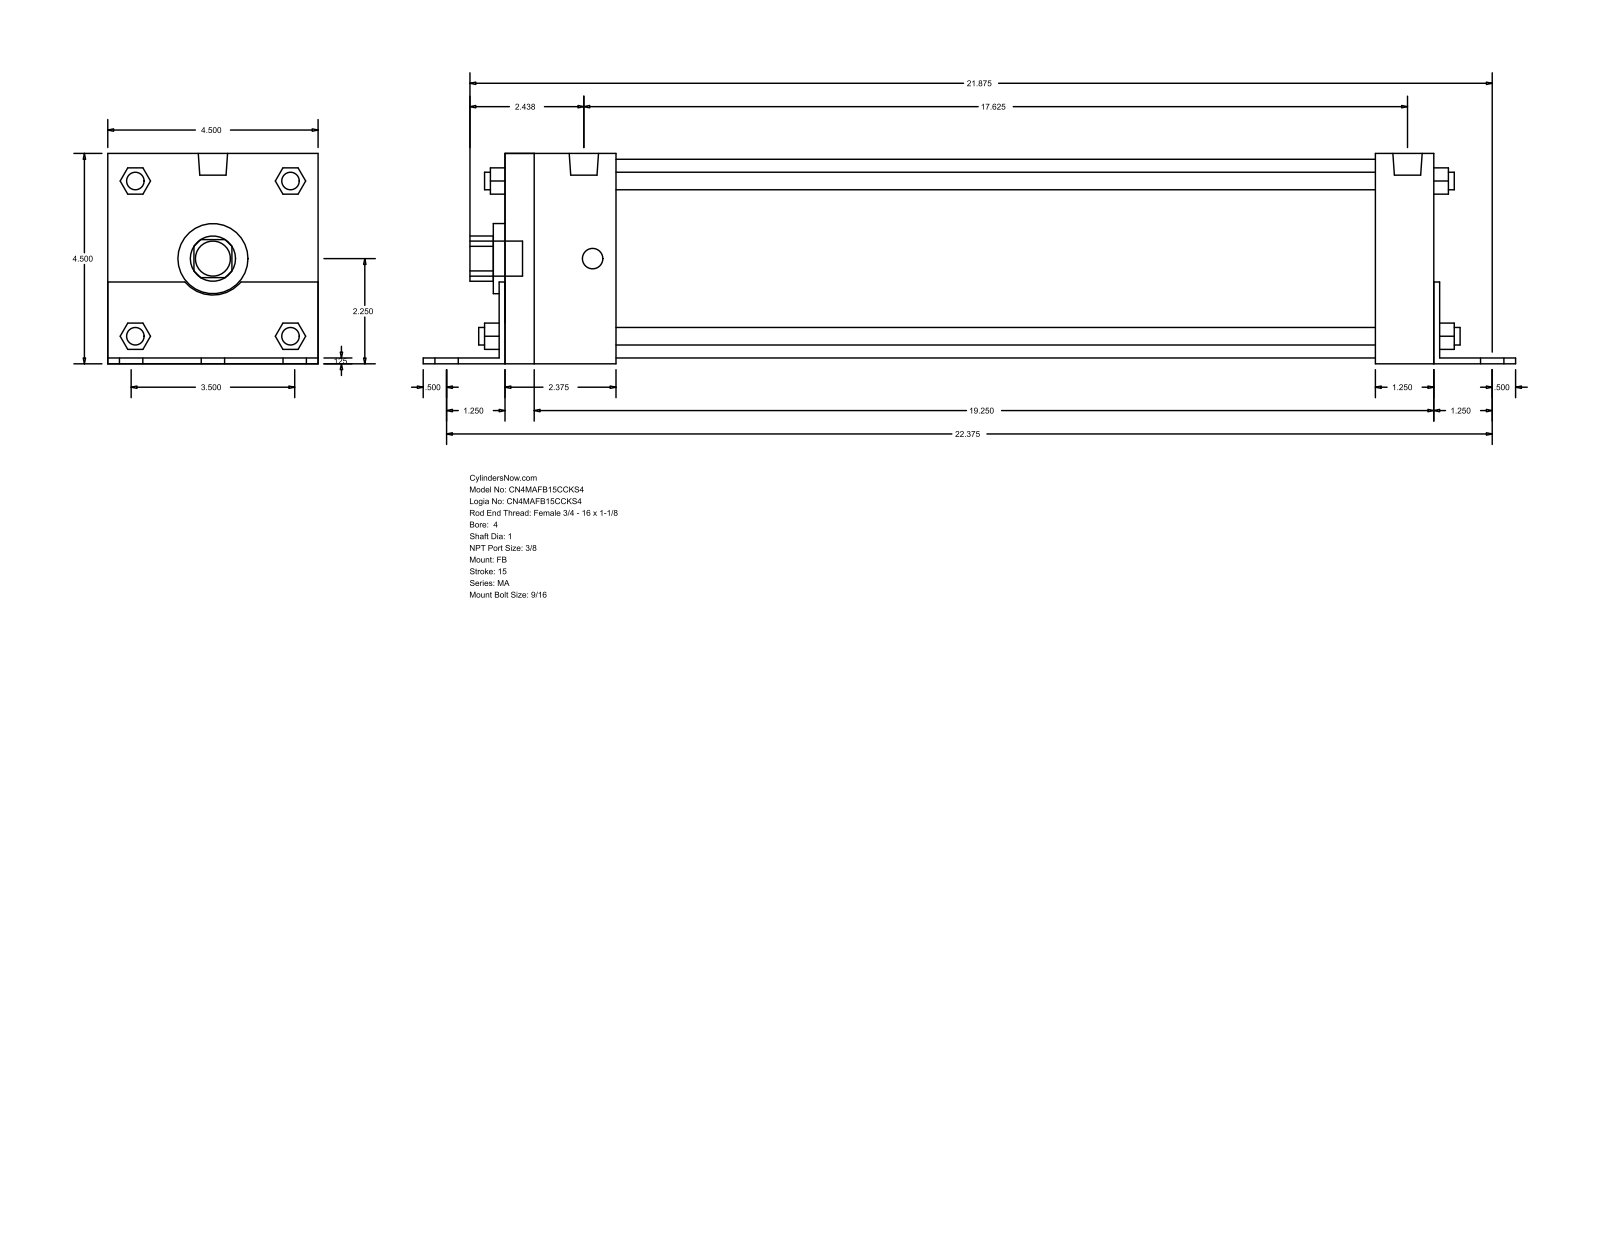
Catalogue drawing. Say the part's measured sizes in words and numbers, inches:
The part is named "MA_FB__0400_1". Its 3-D file was written by "GSSL Pune (CONFIG_CONTROL_DESIGN)". It is 0 solids with 140 faces: 105 planar, 35 cylindrical and 0 other. Overall it measures 23.375 by 4.502 by 4.5 inches. Round holes: 1 of diameter 1, 1 of diameter 1.5, 1 of diameter 4.25. Round bosses or shafts: 6 of diameter 0.563, 4 of diameter 0.437, 4 of diameter 0.375, 2 of diameter 0.627, 1 of diameter 0.75. Partial cylindrical surfaces (rounded edges, fillets, slot ends): 1 of radius 0.484, 1 of radius 0.78. The main face-to-face distances are 4.5, 0.125, 4.502, 20, 0.123, 4.377, 19.875, 20.125, 1.375, 18.75.
